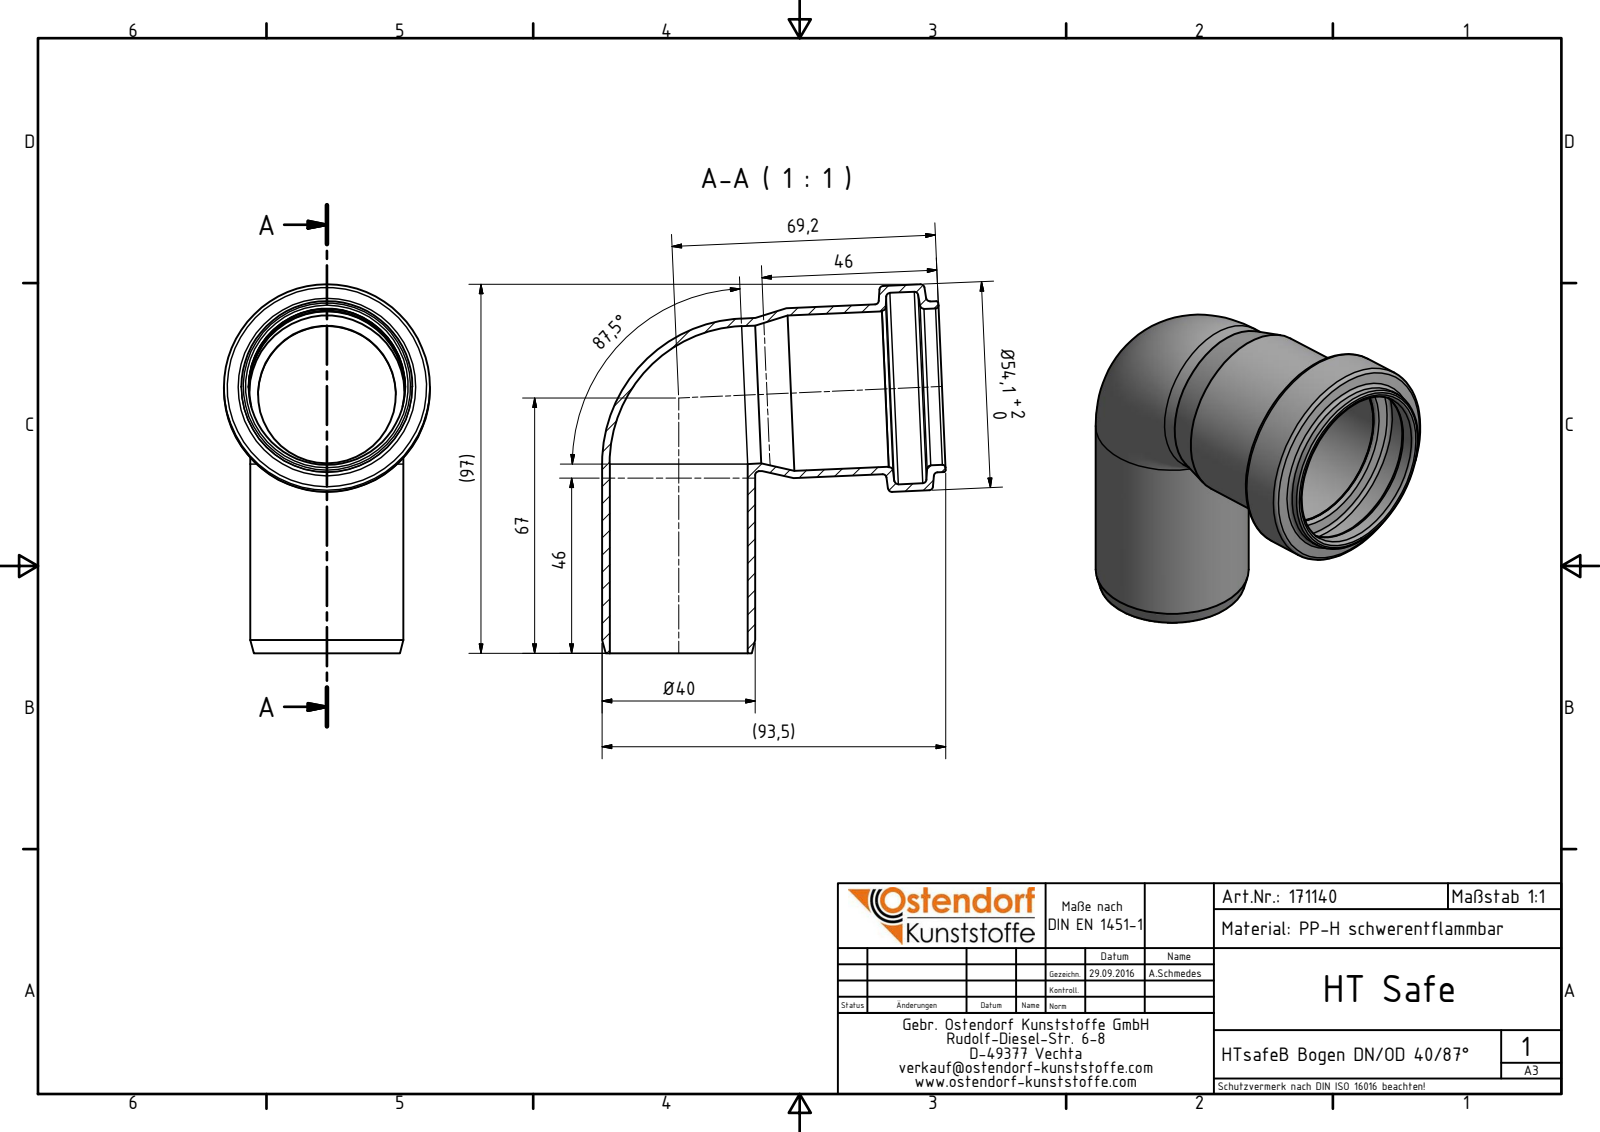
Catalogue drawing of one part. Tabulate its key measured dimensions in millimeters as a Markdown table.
| quantity | value |
| --- | --- |
| part name | 171140 HTsafeB DN_OD 40_87° |
| STEP written by | Autodesk Inventor 2016 (AUTOMOTIVE_DESIGN) |
| units | millimeters |
| bodies | 1 solid, 34 faces (3 planar, 11 cylindrical, 20 other) |
| overall size | 96.85 × 90.19 × 54.1 |
| volume | 32 860 mm³ |
| surface area | 35 384 mm² |
| round holes (diameter × count) | 36.2 × 2, 41.1 × 2, 40.8 × 1, 50.3 × 1 |
| round bosses / shafts (diameter × count) | 40.2 × 2, 54.1 × 1, 44.9 × 1, 44.6 × 1 |
| main face-to-face distances | 14.9 |
